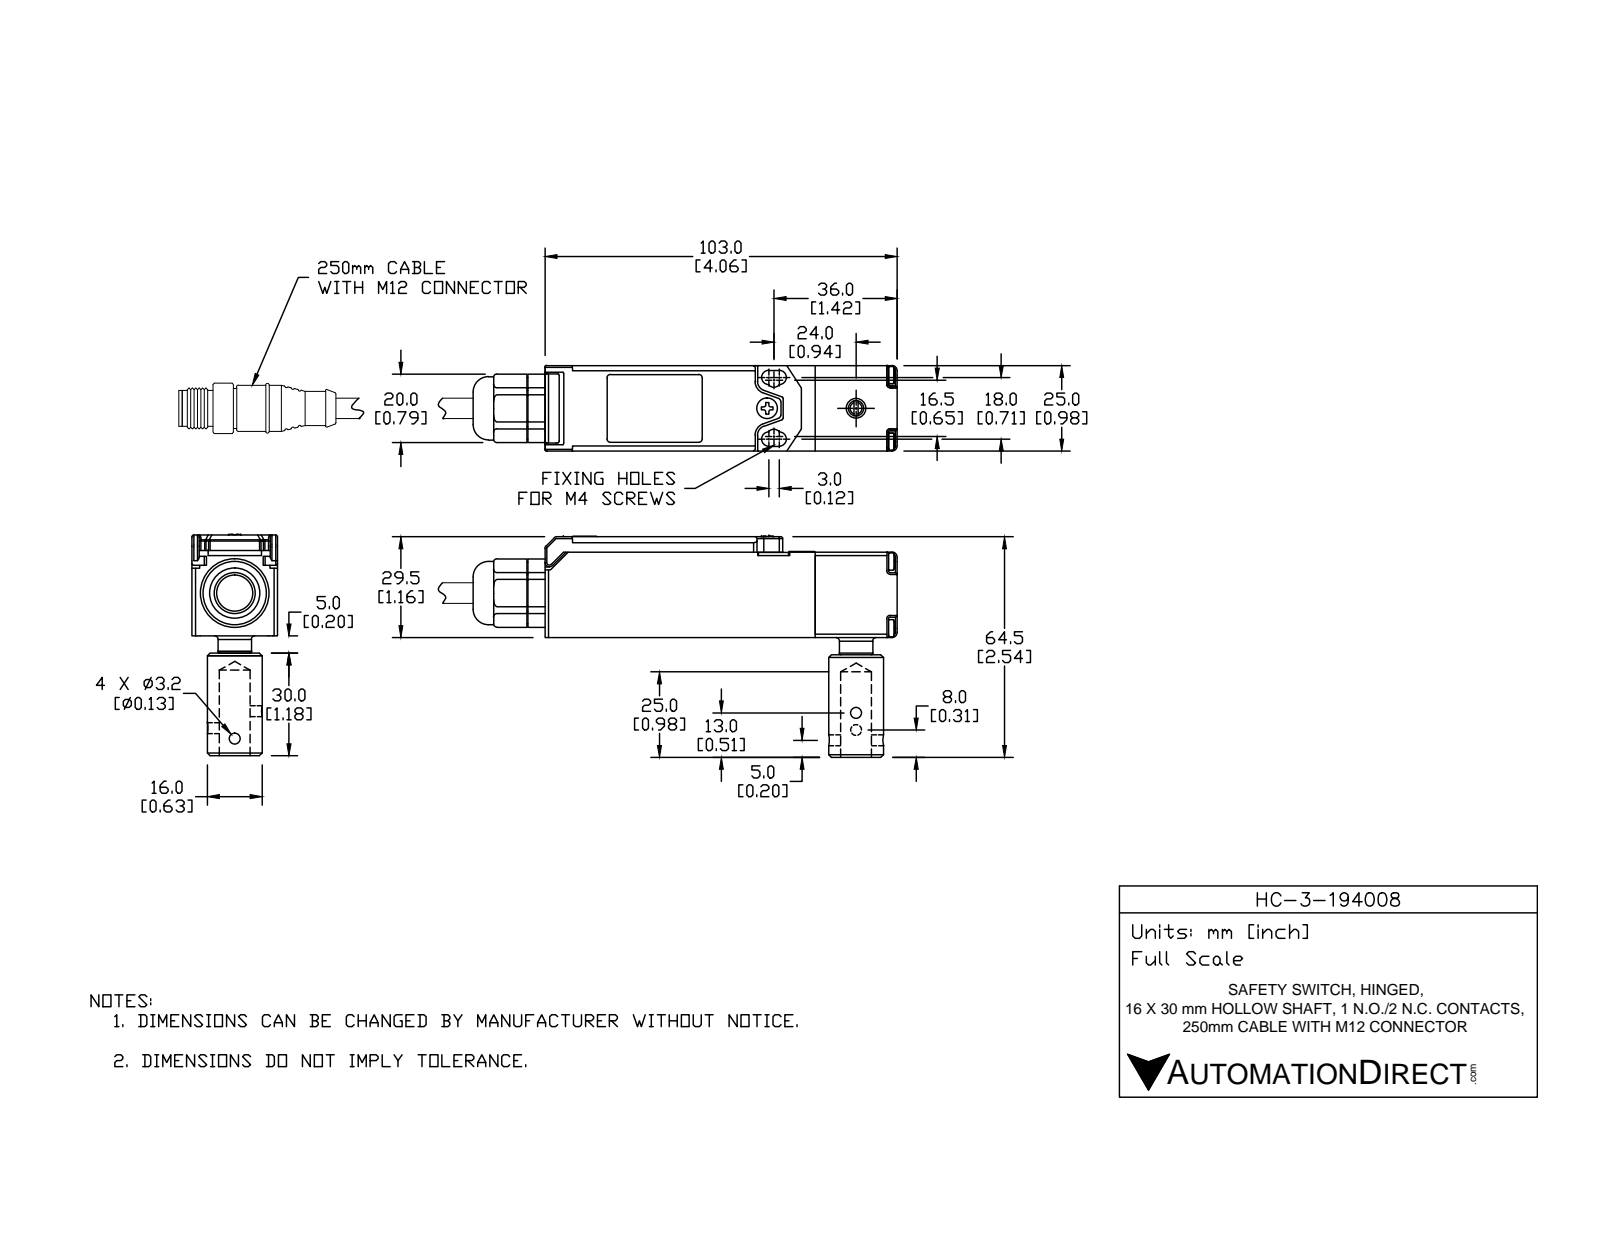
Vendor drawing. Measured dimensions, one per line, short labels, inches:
name: HC-3-194008
written by: SolidWorks 2014 (AUTOMOTIVE_DESIGN)
unit: in
bodies: 13 solids, 1862 faces (866 planar, 593 cylindrical, 403 other)
size: 4.055 × 2.549 × 0.984
volume: 2.095 in³; area: 52.91 in²
holes: 8× ⌀0.126, 4× ⌀0.094, 2× ⌀0.059, 2× ⌀0.063, 2× ⌀0.071, 2× ⌀0.087, 2× ⌀0.142, 2× ⌀0.63, 1× ⌀0.055, 1× ⌀0.081, 1× ⌀0.098, 1× ⌀0.102
bosses: 5× ⌀0.102, 4× ⌀0.197, 4× ⌀0.079, 2× ⌀0.138, 1× ⌀0.63, 1× ⌀0.386, 1× ⌀0.256, 1× ⌀0.228
rounds: 225× R0.02, 24× R0.004, 21× R0.039, 12× R0.012, 6× R0.059, 6× R0.083, 6× R0.11, 6× R0.138
face distances: 0.984, 0.079, 0.071, 0.913, 0.177, 0.906, 0.098, 0.039, 0.827, 0.087
hole spacings: 0.543, 0.768, 0.171, 0.187, 0.245, 0.414, 0.423, 0.426
